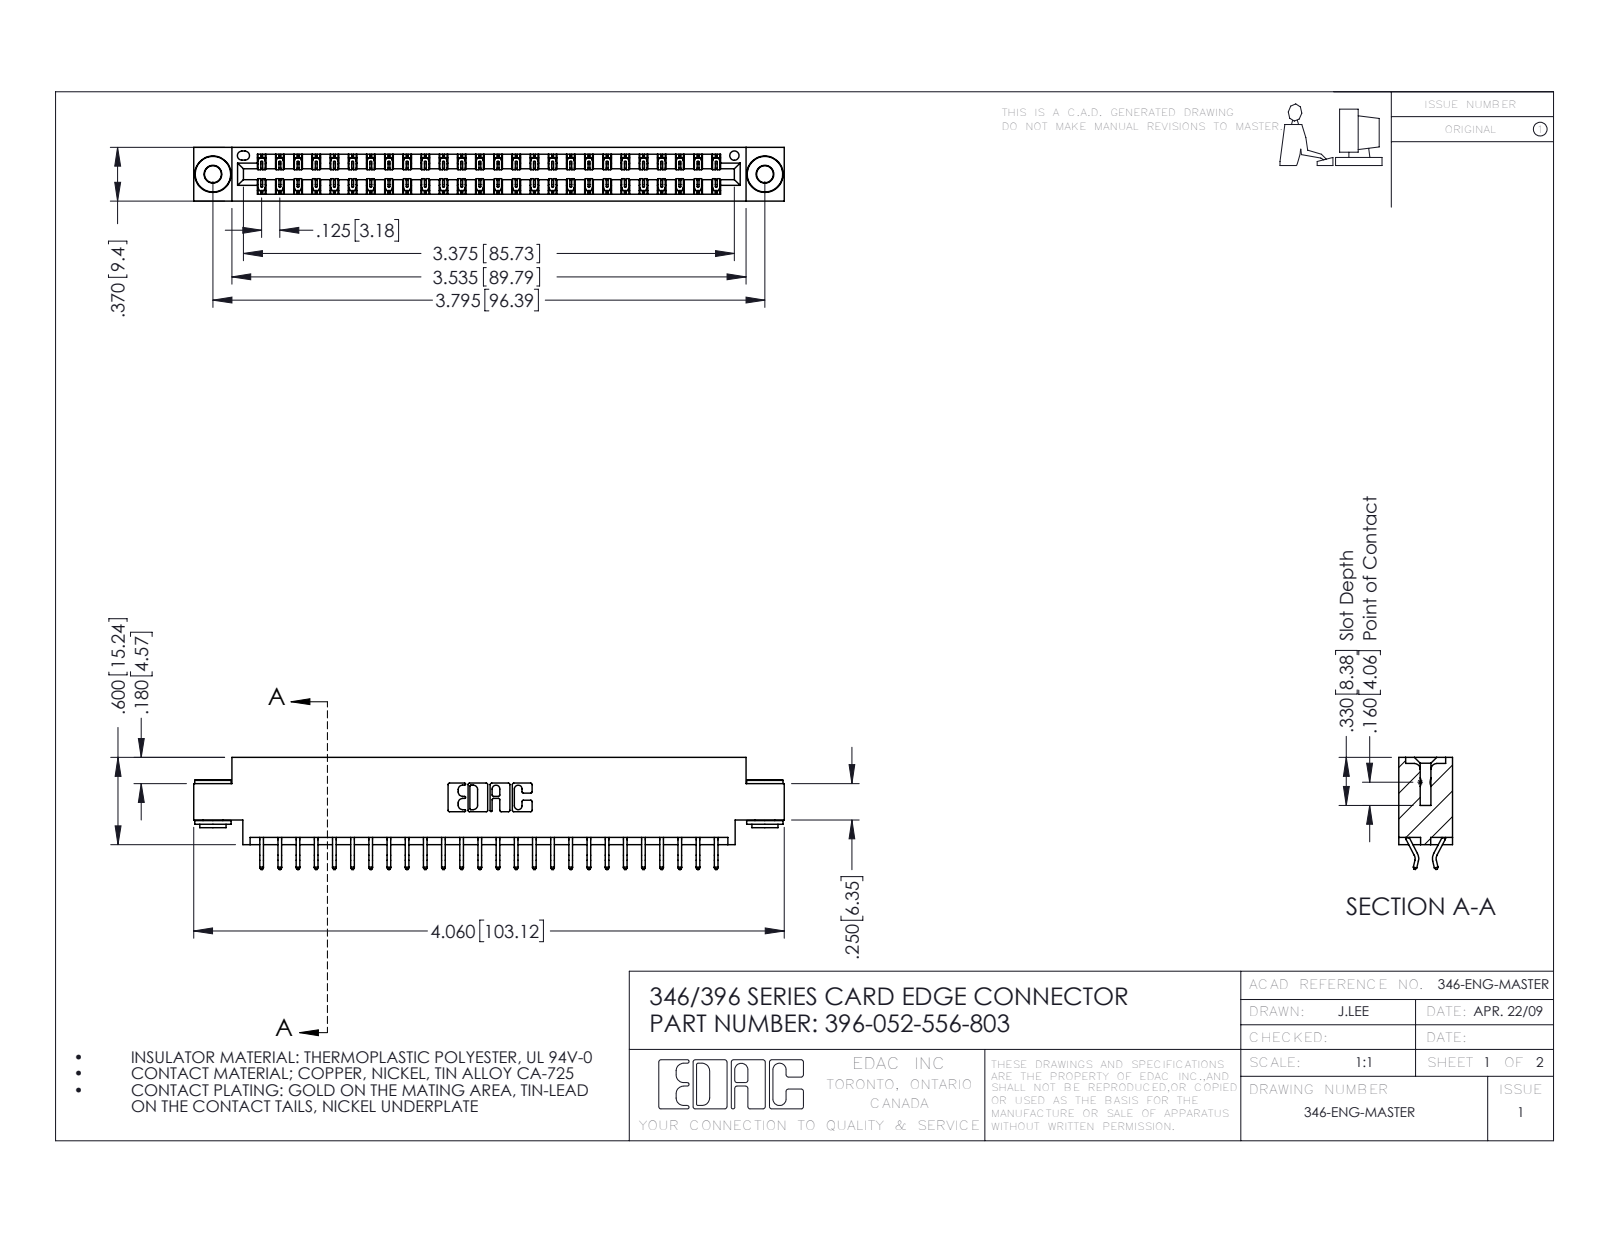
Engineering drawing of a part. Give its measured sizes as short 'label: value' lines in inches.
name: 345-292-001_556 Tail; 345-250-002_345-250-002-102; 396-052-556-803; 346 Part_0.170 Offset - 0.156 Dia-TH
written by: SolidWorks 2016 (CONFIG_CONTROL_DESIGN)
unit: in
bodies: 55 solids, 3180 faces (2118 planar, 1054 cylindrical, 8 other)
size: 4.06 × 0.77 × 0.37
volume: 0.598 in³; area: 21.01 in²
holes: 2× ⌀0.116, 2× ⌀0.156, 1× ⌀0.064
bosses: 2× ⌀0.25, 2× ⌀0.18, 2× ⌀0.136
rounds: 78× R0.006, 22× R0.01, 6× R0.007, 6× R0.031, 3× R0.026, 2× R0.01, 2× R0.014, 2× R0.022
face distances: 0.048, 0.322, 0.37, 0.25, 0.025, 0.275, 0.072, 0.298, 0.148, 0.222
hole spacings: 0.246, 3.587, 3.795
